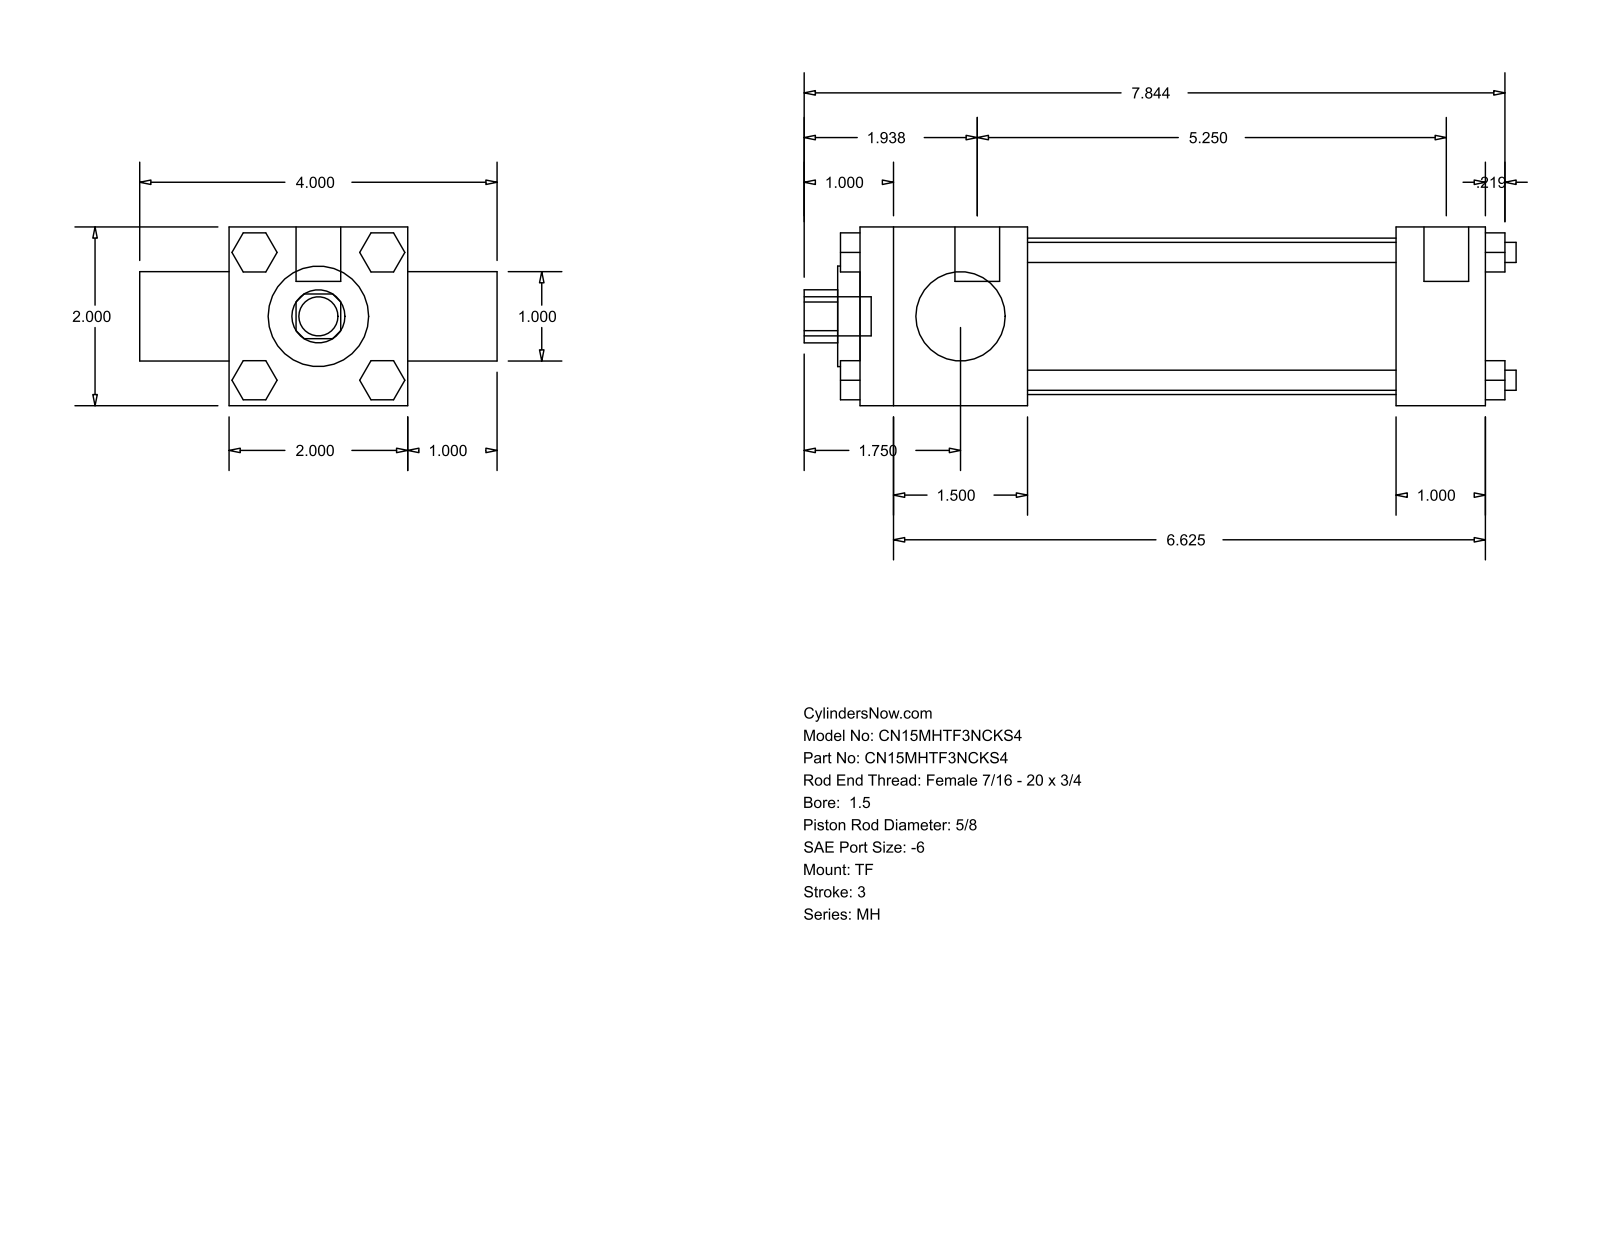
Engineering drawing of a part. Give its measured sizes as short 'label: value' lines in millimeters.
name: MH_TF__0150_0.625
written by: GSSL Pune (CONFIG_CONTROL_DESIGN)
unit: mm
bodies: 0 solids, 120 faces (92 planar, 28 cylindrical, 0 other)
size: 202.41 × 101.6 × 50.8
holes: 1× ⌀15.88, 1× ⌀25.4, 1× ⌀28.57, 1× ⌀44.45
bosses: 4× ⌀5.71, 3× ⌀5.56, 2× ⌀12.7, 1× ⌀11.11
rounds: 1× R7.54
face distances: 50.8, 25.4, 177.8, 76.2, 47.62, 130.18, 152.4, 104.78, 11.11, 18.16
